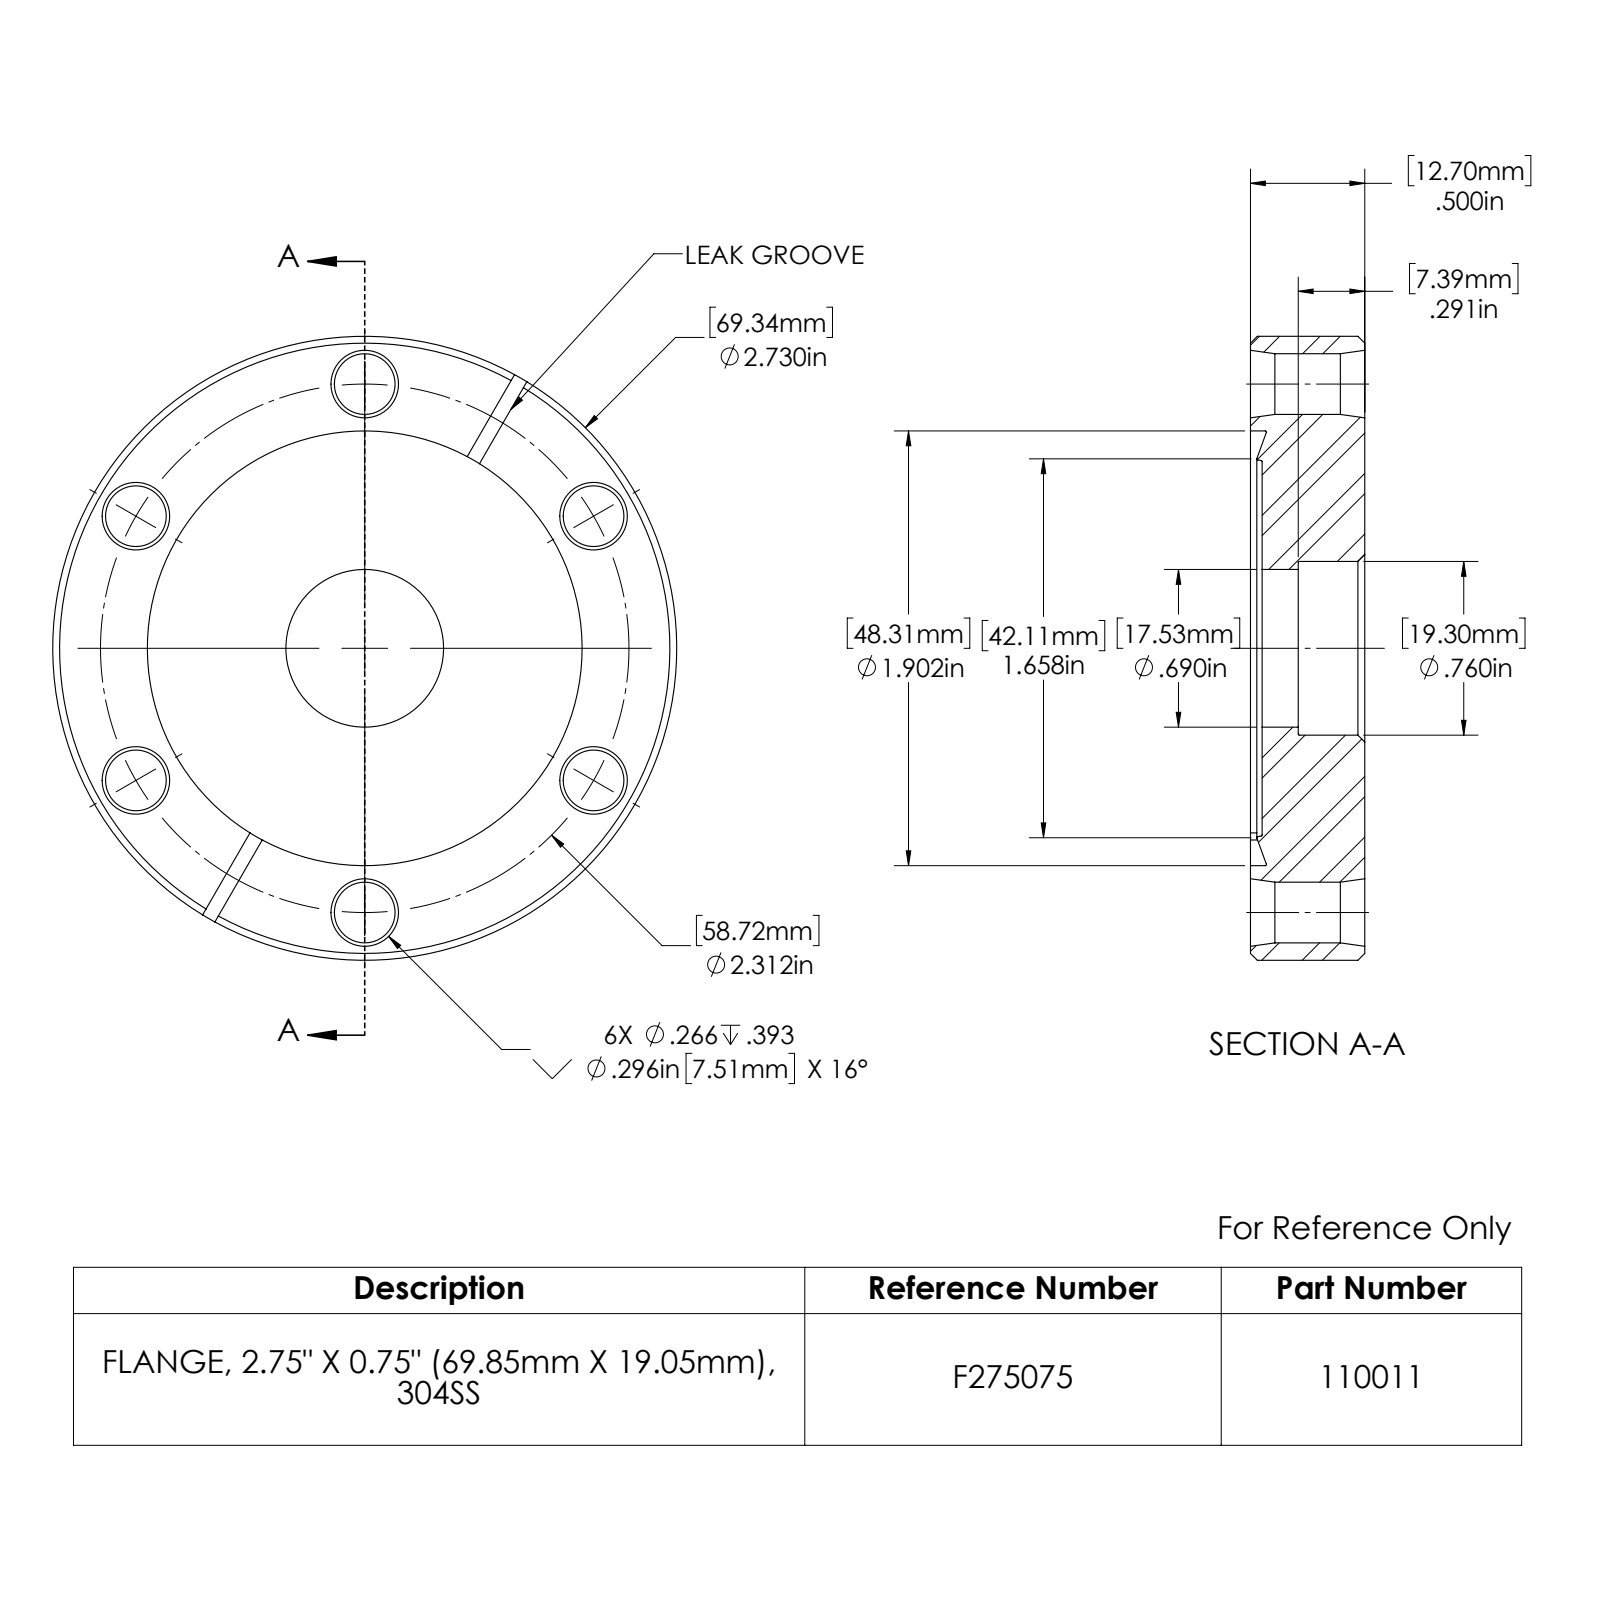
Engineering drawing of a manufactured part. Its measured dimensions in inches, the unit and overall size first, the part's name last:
Units: inches
Overall size (bounding box): 2.73 × 2.73 × 0.5
Round holes (diameter × count): ⌀0.266 ×6, ⌀0.69 ×1, ⌀0.76 ×1, ⌀1.902 ×1
Round bosses / shafts (diameter × count): ⌀2.73 ×1
Main face-to-face distances: 0.5, 0.051, 0.449, 0.209, 0.158, 0.291, 0.052, 0.157, 0.448, 0.062
Hole centre spacings: 1.156, 2.002, 2.002, 2.312, 2.312
Volume: 2.406 in³ · Surface area: 18.29 in²
Bodies: 1 solid, 74 faces (11 planar, 20 cylindrical, 43 other)
Part name (STEP PRODUCT): 110011_A
STEP written by: SolidWorks 2022 (CONFIG_CONTROL_DESIGN)
